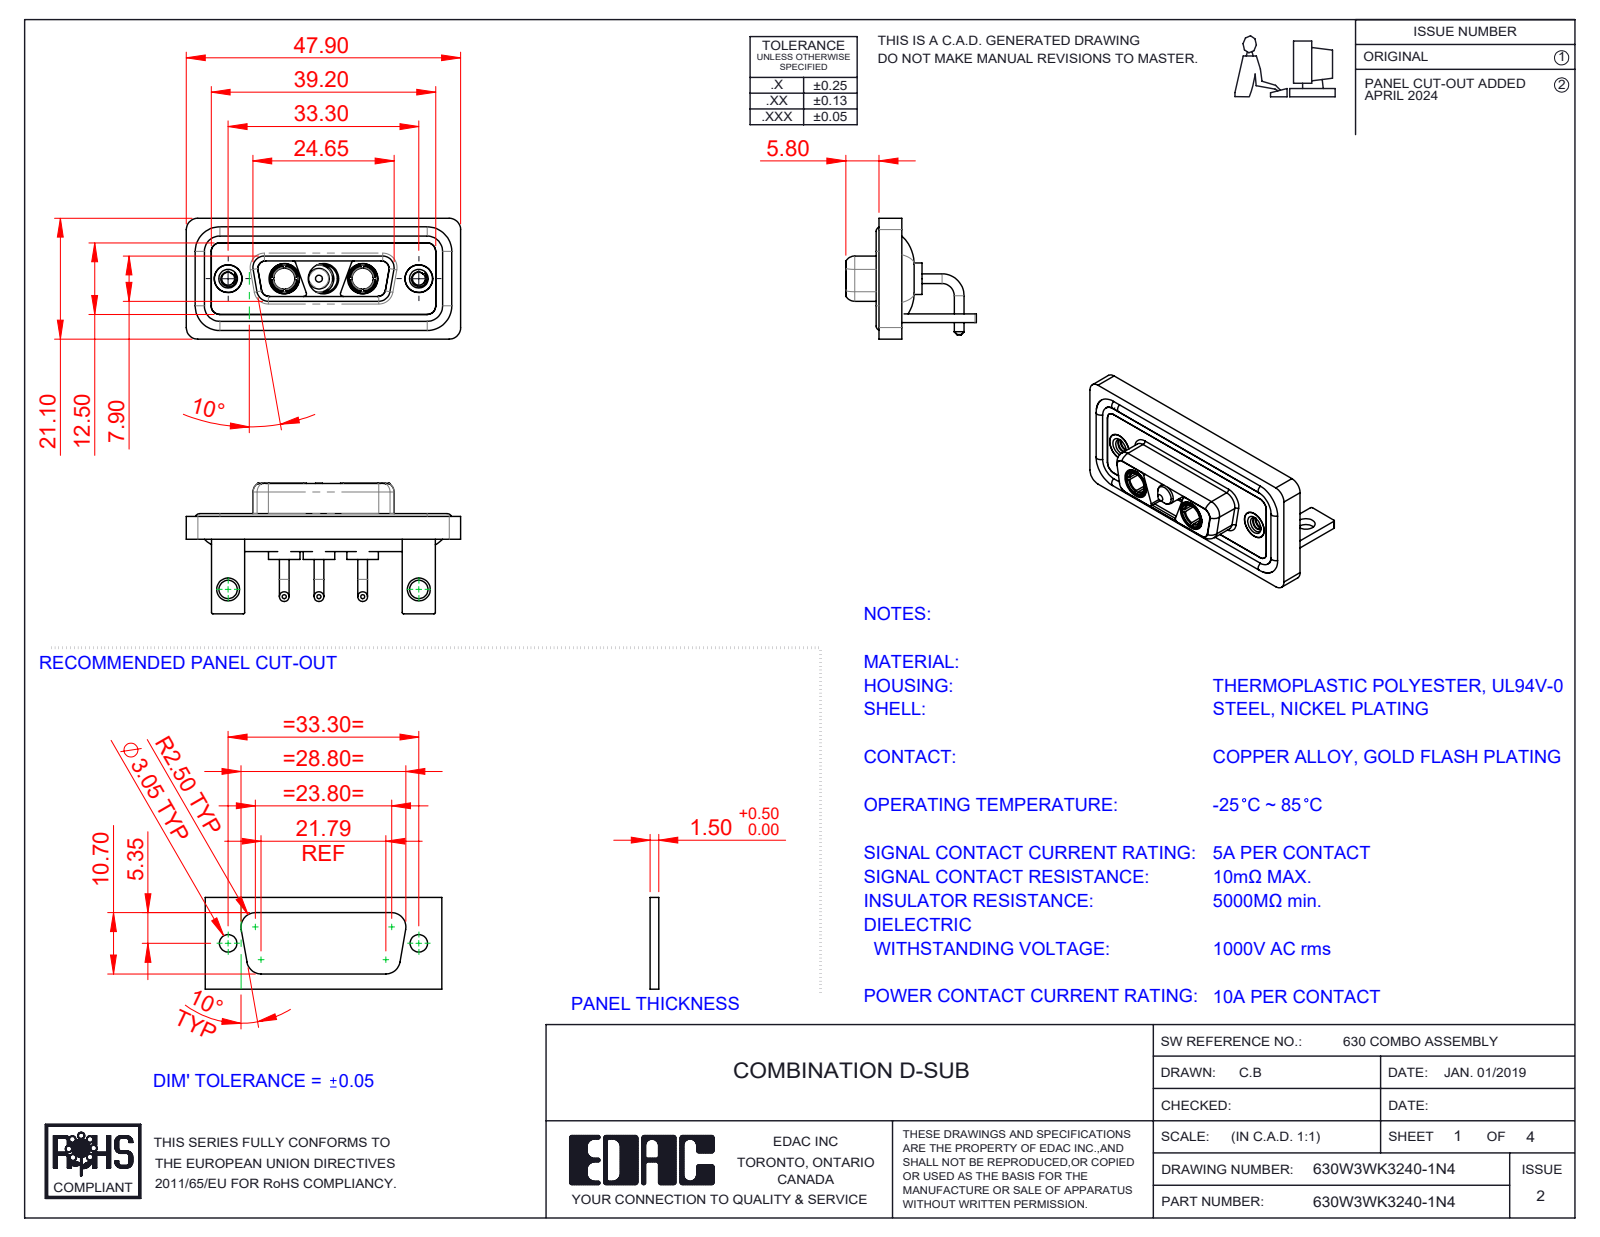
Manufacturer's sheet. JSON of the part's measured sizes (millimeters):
{"part_name": "630Combo Waterproof Housing_15 Contacts; 630Combo Threaded Rivet_2; 630W3WK3240-1N4; 630Combo Shell Rear_15 Contacts (+5 more)", "step_written_by": "SolidWorks 2023 (CONFIG_CONTROL_DESIGN)", "units": "millimeters", "bodies": {"solids": 15, "faces": 643, "planar": 198, "cylindrical": 288, "other": 157}, "overall_size": [47.9, 22.8, 21.1], "volume_mm3": 6225, "surface_area_mm2": 10321, "round_holes": [[4.85, 5], [5.3, 3], [2.26, 2], [3.2, 2], [3.7, 2], [4, 2], [4.05, 2], [5, 2]], "round_bosses_or_shafts": [[1.7, 6], [1.6, 4], [5.5, 3], [5.2, 3], [4.75, 3], [3.75, 3], [4.96, 2], [4.95, 2]], "partial_cylinders_radius": [[2, 21], [1.5, 18], [0.25, 16], [1.35, 12], [0.5, 9], [1.6, 8], [0.6, 4], [0.65, 4]], "face_to_face_distances": [0.4, 2.9, 1.5, 3.7, 1.8, 1.1, 4.1, 1.6, 2.5, 1.4], "hole_center_spacings": [6.85, 9.8, 16.65, 23.5, 33.3, 13.7]}
